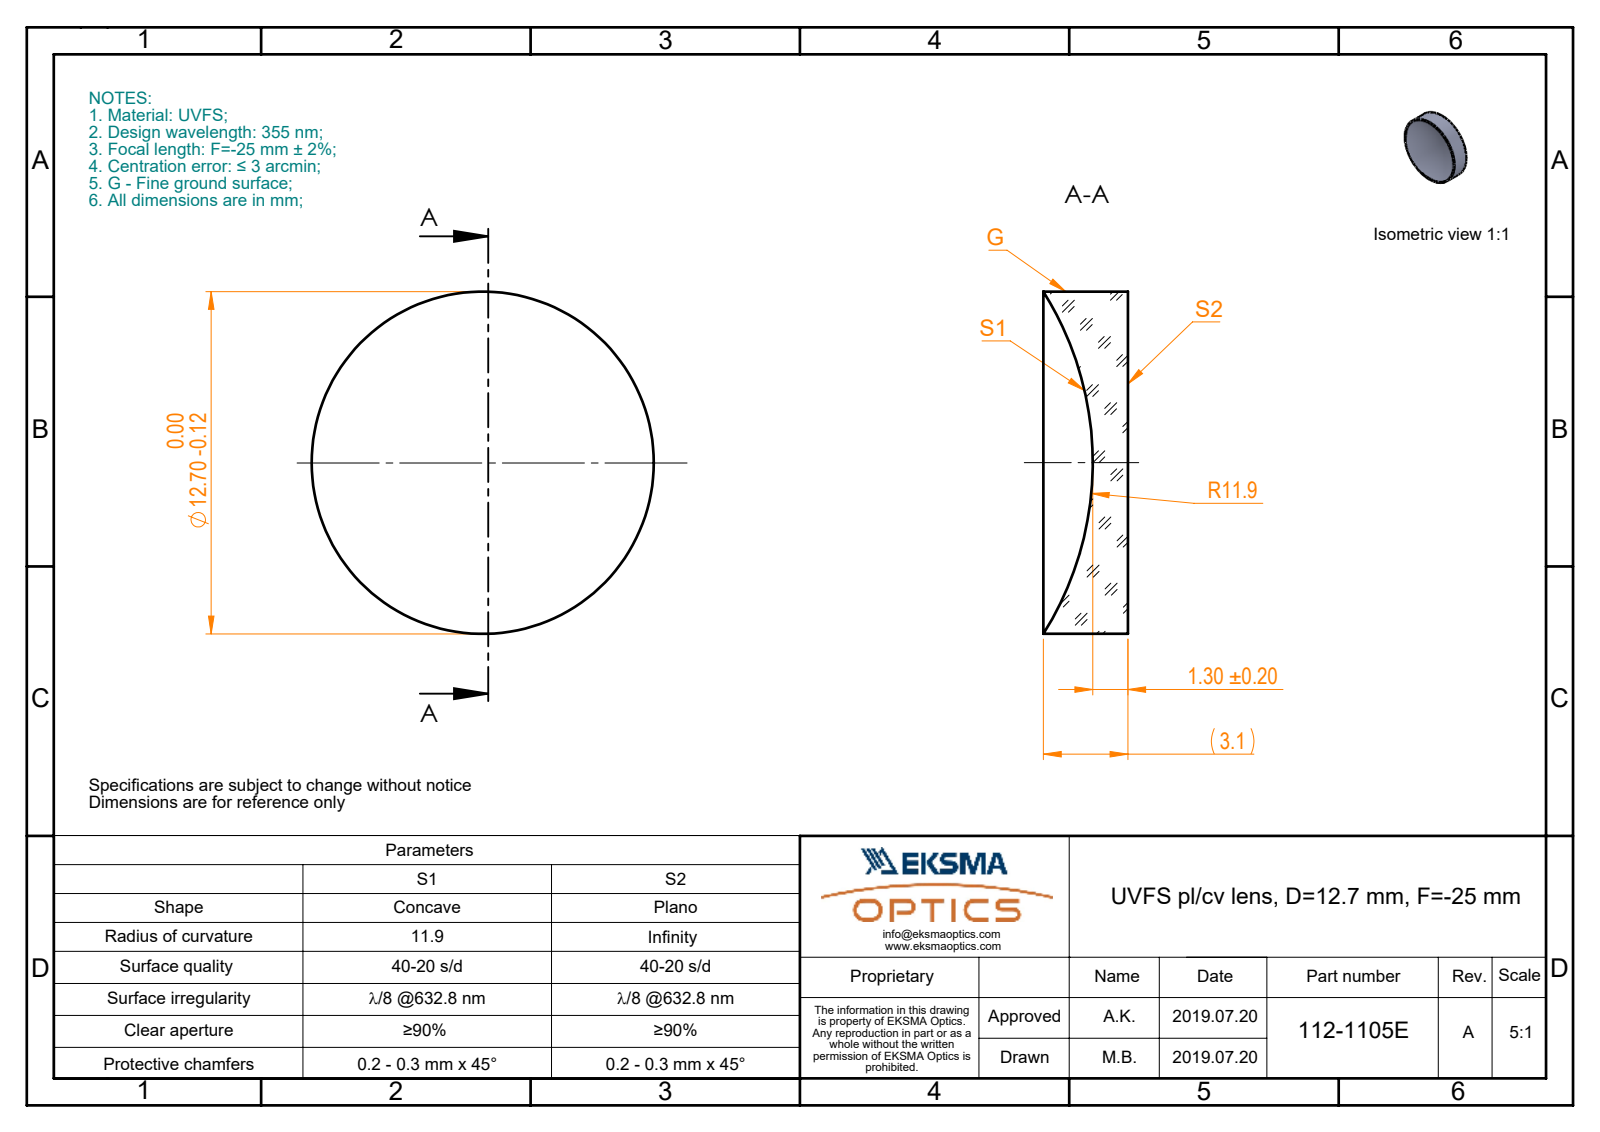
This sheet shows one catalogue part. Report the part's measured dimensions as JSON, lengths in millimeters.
{"part_name": "112-1105E UVFS pl-cv 12.7 F-25", "step_written_by": "SolidWorks 2017 (CONFIG_CONTROL_DESIGN)", "units": "millimeters", "bodies": {"solids": 1, "faces": 5, "planar": 1, "cylindrical": 2, "other": 2}, "overall_size": [12.7, 12.7, 3.14], "volume_mm3": 278, "surface_area_mm2": 389, "round_bosses_or_shafts": [[12.7, 1]]}
